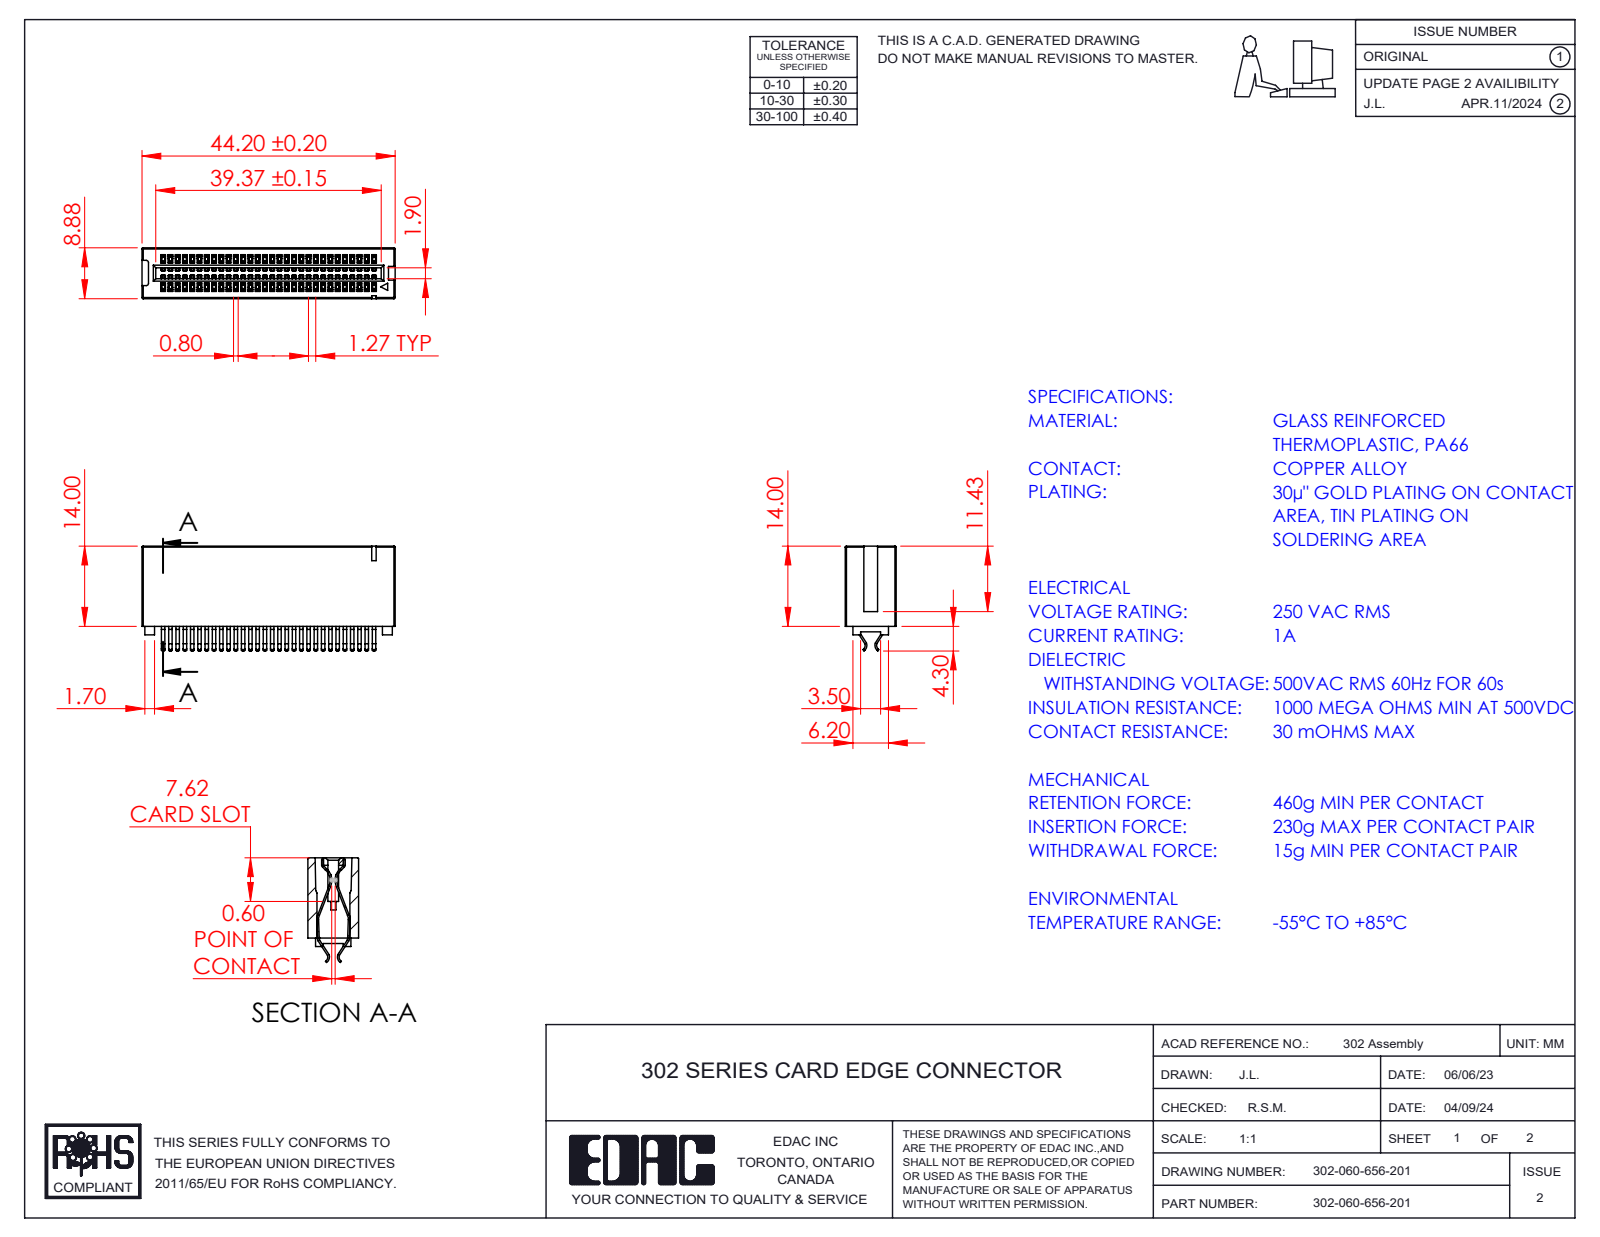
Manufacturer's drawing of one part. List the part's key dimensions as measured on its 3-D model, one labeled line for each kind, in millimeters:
Part name (STEP PRODUCT): Contact_302-290-X56; HSG_Vertical HSG; 302-060-656-201
STEP written by: SolidWorks 2023 (CONFIG_CONTROL_DESIGN)
Units: millimetres
Bodies: 61 solids, 2916 faces (1939 planar, 973 cylindrical, 4 other)
Overall size (bounding box): 44.2 × 18.3 × 8.88
Volume: 3 475 mm³ · Surface area: 9 399 mm²
Partial cylindrical surfaces — rounded edges, fillets, slot ends (radius × count): R0.2 ×188, R0.11 ×2, R0.4 ×2, R0.41 ×2, R0.93 ×2, R1.05 ×2, R1.23 ×2, R1.25 ×2
Main face-to-face distances: 8.88, 1.27, 2.54, 3.81, 7.62, 3.8, 5.08, 6.35, 1.9, 5.07
